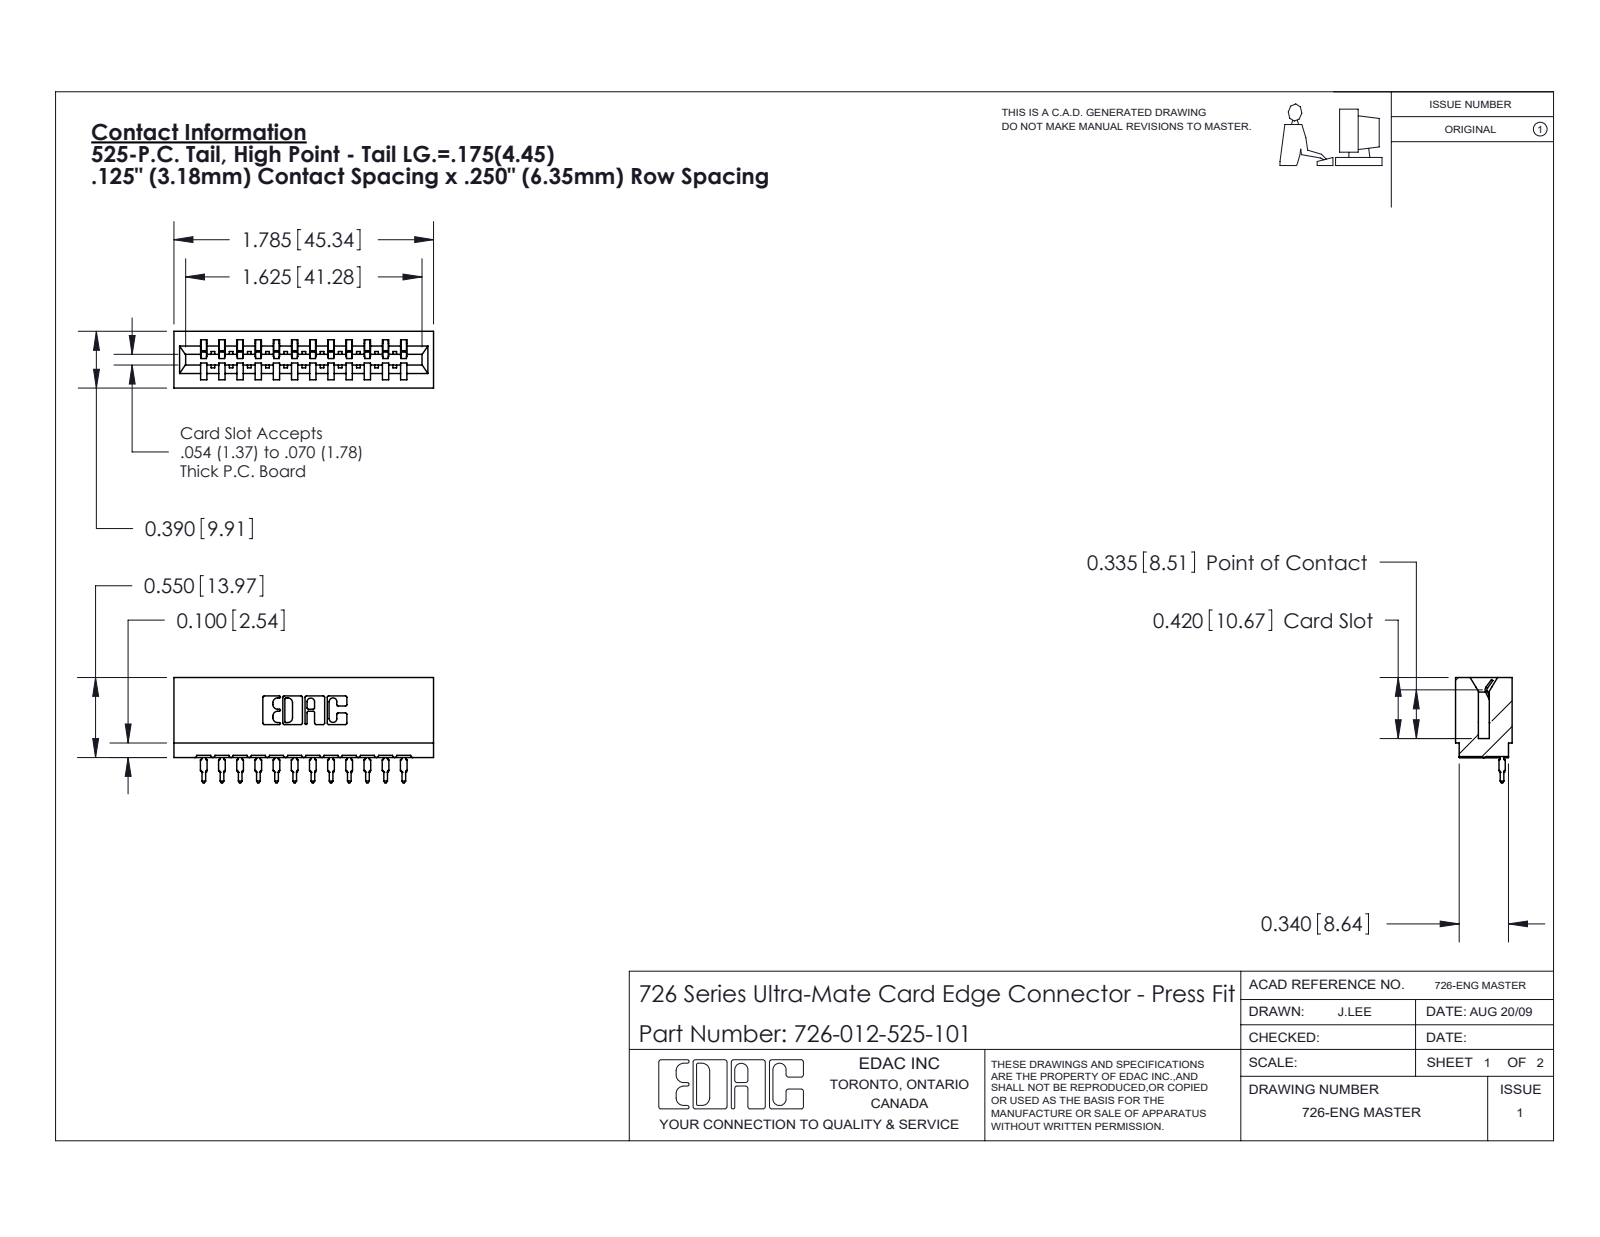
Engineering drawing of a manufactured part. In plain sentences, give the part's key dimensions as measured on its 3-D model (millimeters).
The part is named "746-292-001_525; 726-012-525-101; 726 Part_.515 Slot Depth - 01". Its 3-D file was written by "SolidWorks 2020 (CONFIG_CONTROL_DESIGN)". It is 13 solids with 1393 faces: 811 planar, 270 cylindrical and 312 other. Overall it measures 45.3 by 18.4 by 9.9 millimeters. Its volume is 4 210 cubic millimeters and its surface area 5 919 square millimeters. Partial cylindrical surfaces (rounded edges, fillets, slot ends): 24 of radius 0.5, 22 of radius 0.3, 13 of radius 0.4, 6 of radius 0.2, 6 of radius 0.8, 4 of radius 0.1, 4 of radius 0.3, 3 of radius 0.7. The main face-to-face distances are 6.4, 8.5, 1.4, 12.7, 9.9, 3.2, 19.1, 3.2, 7.4, 1.1.
